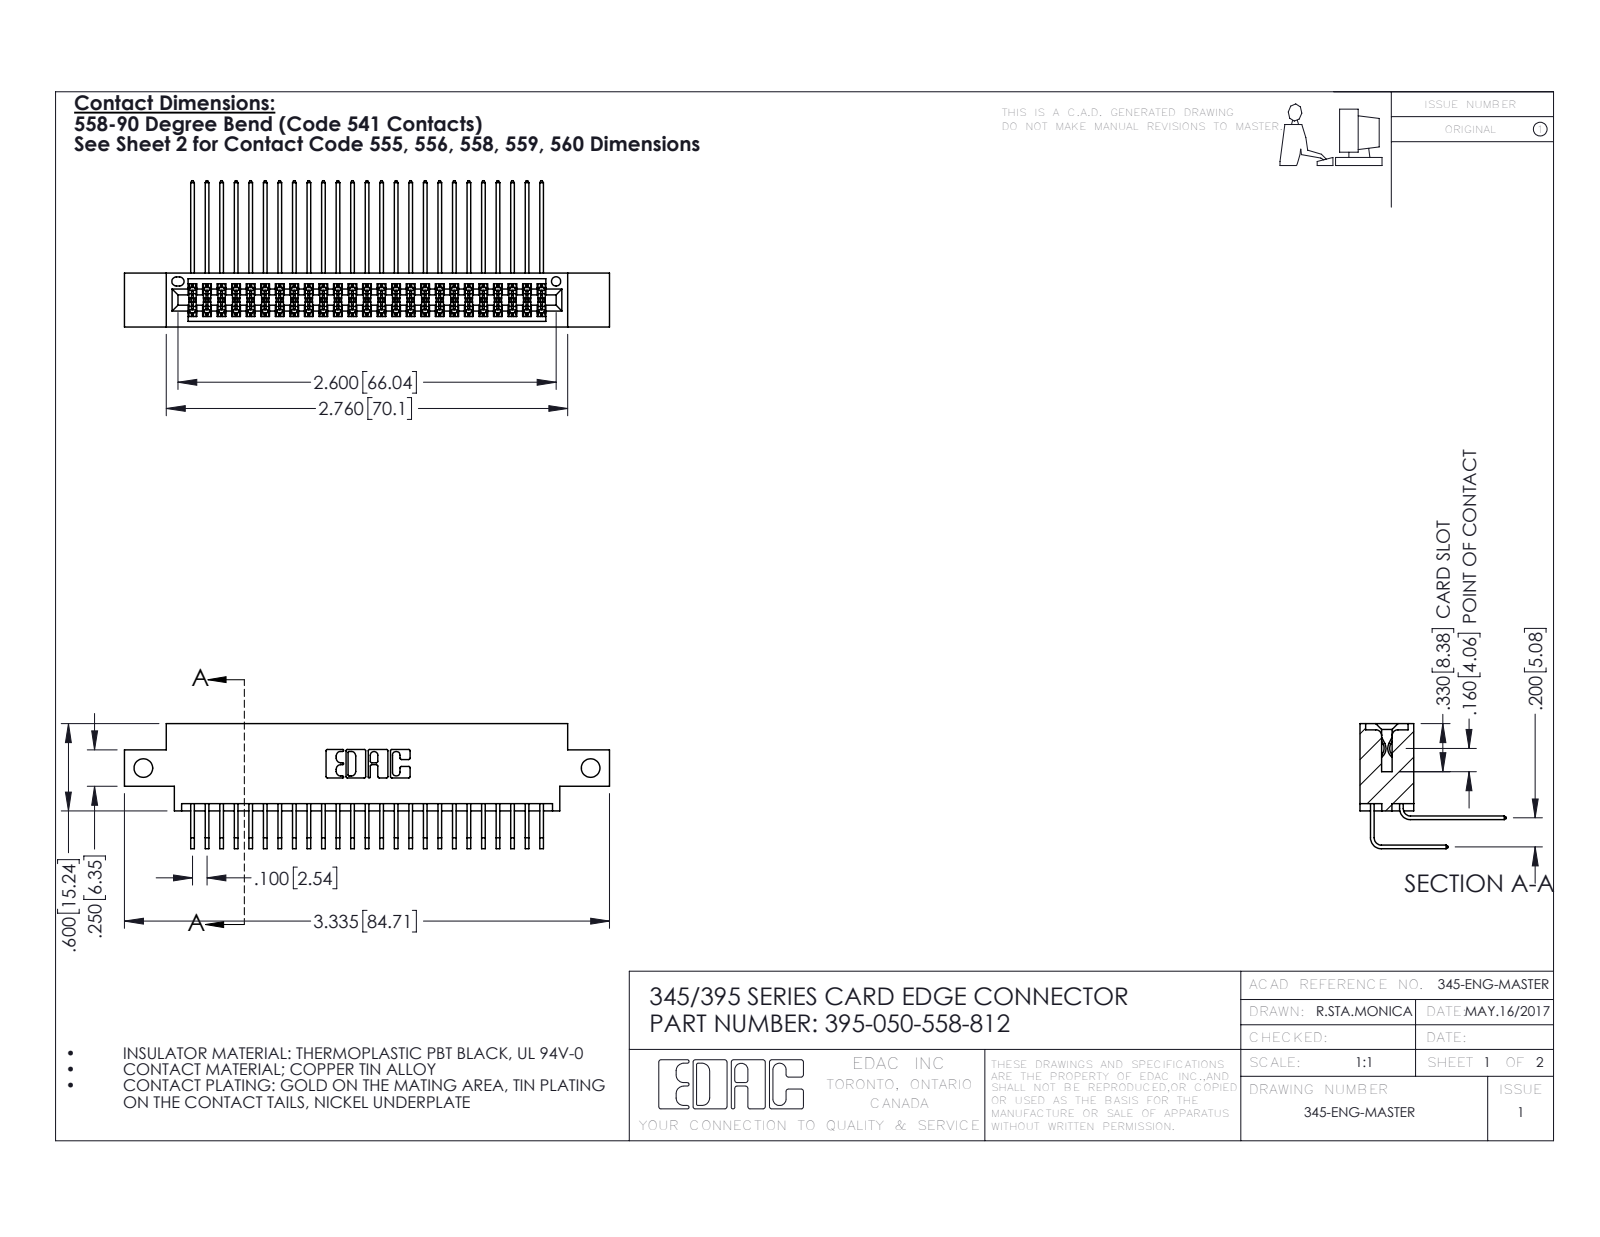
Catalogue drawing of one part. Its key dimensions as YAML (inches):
part_name: "345-292-001_558 Tail - 2; 395-050-558-812; 345-292-001_558 559 Tail - 1; 345 Part_0.170 Offset - Side Mount"
step_written_by: "SolidWorks 2016 (CONFIG_CONTROL_DESIGN)"
units: inches
bodies: {solids: 51, faces: 2730, planar: 1834, cylindrical: 896, other: 0}
overall_size: [3.335, 1.005, 0.859]
volume: 0.498
surface_area: 20.3
round_holes:
  - {diameter: 0.128, count: 2}
  - {diameter: 0.064, count: 1}
partial_cylinders:
  - {radius: 0.006, count: 76}
  - {radius: 0.01, count: 22}
  - {radius: 0.007, count: 6}
  - {radius: 0.031, count: 6}
  - {radius: 0.026, count: 3}
  - {radius: 0.014, count: 2}
  - {radius: 0.019, count: 2}
  - {radius: 0.022, count: 2}
face_to_face_distances: [0.072, 0.298, 0.2, 0.37, 0.098, 0.272, 0.025, 0.225, 0.175, 0.025]
hole_center_spacings: [3.075]
